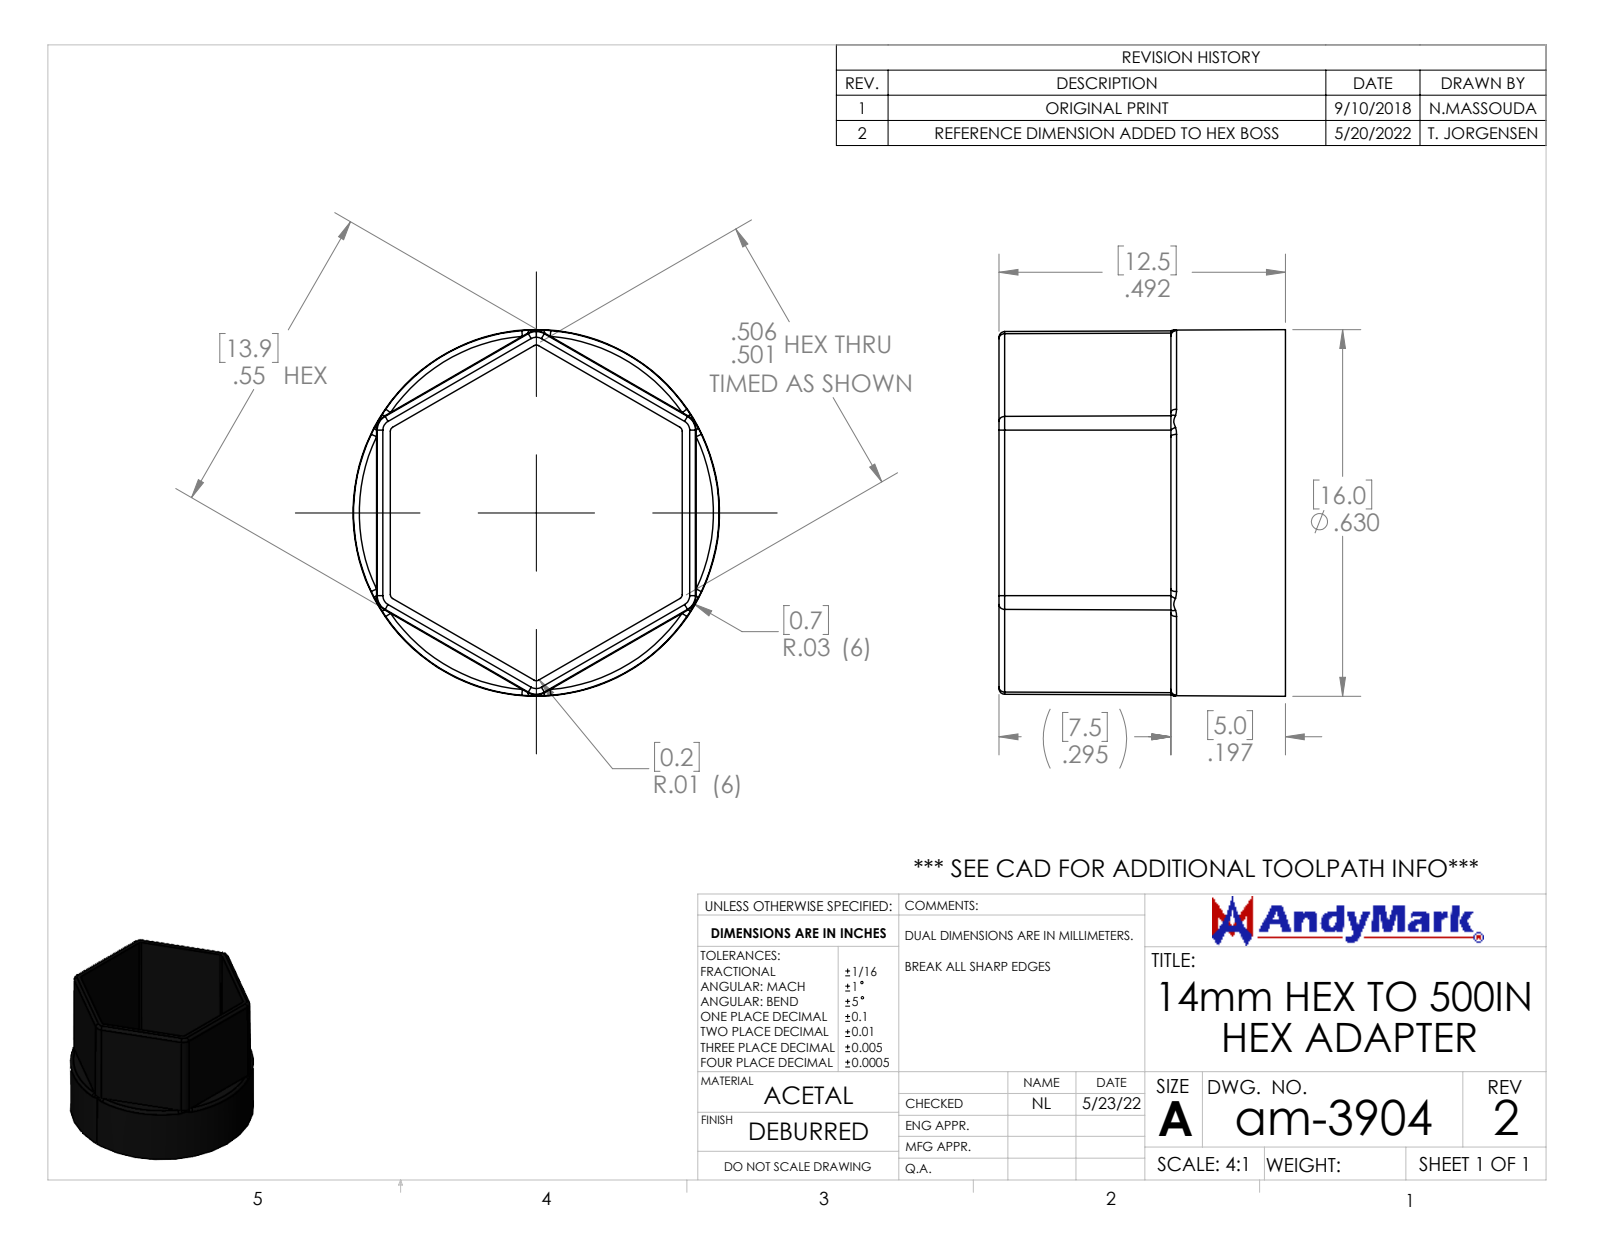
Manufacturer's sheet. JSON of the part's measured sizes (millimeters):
{"part_name": "am-3904 14mm Hex to 500in Hex", "step_written_by": "SolidWorks 2021 (CONFIG_CONTROL_DESIGN)", "units": "millimeters", "bodies": {"solids": 1, "faces": 93, "planar": 27, "cylindrical": 12, "other": 54}, "overall_size": [16, 16, 12.5], "volume_mm3": 487, "surface_area_mm2": 1266, "partial_cylinders_radius": [[0.1, 6], [0.25, 6]], "face_to_face_distances": [0.58, 5, 12.5, 7.5, 4.8, 12.3, 1.1, 1.32]}
